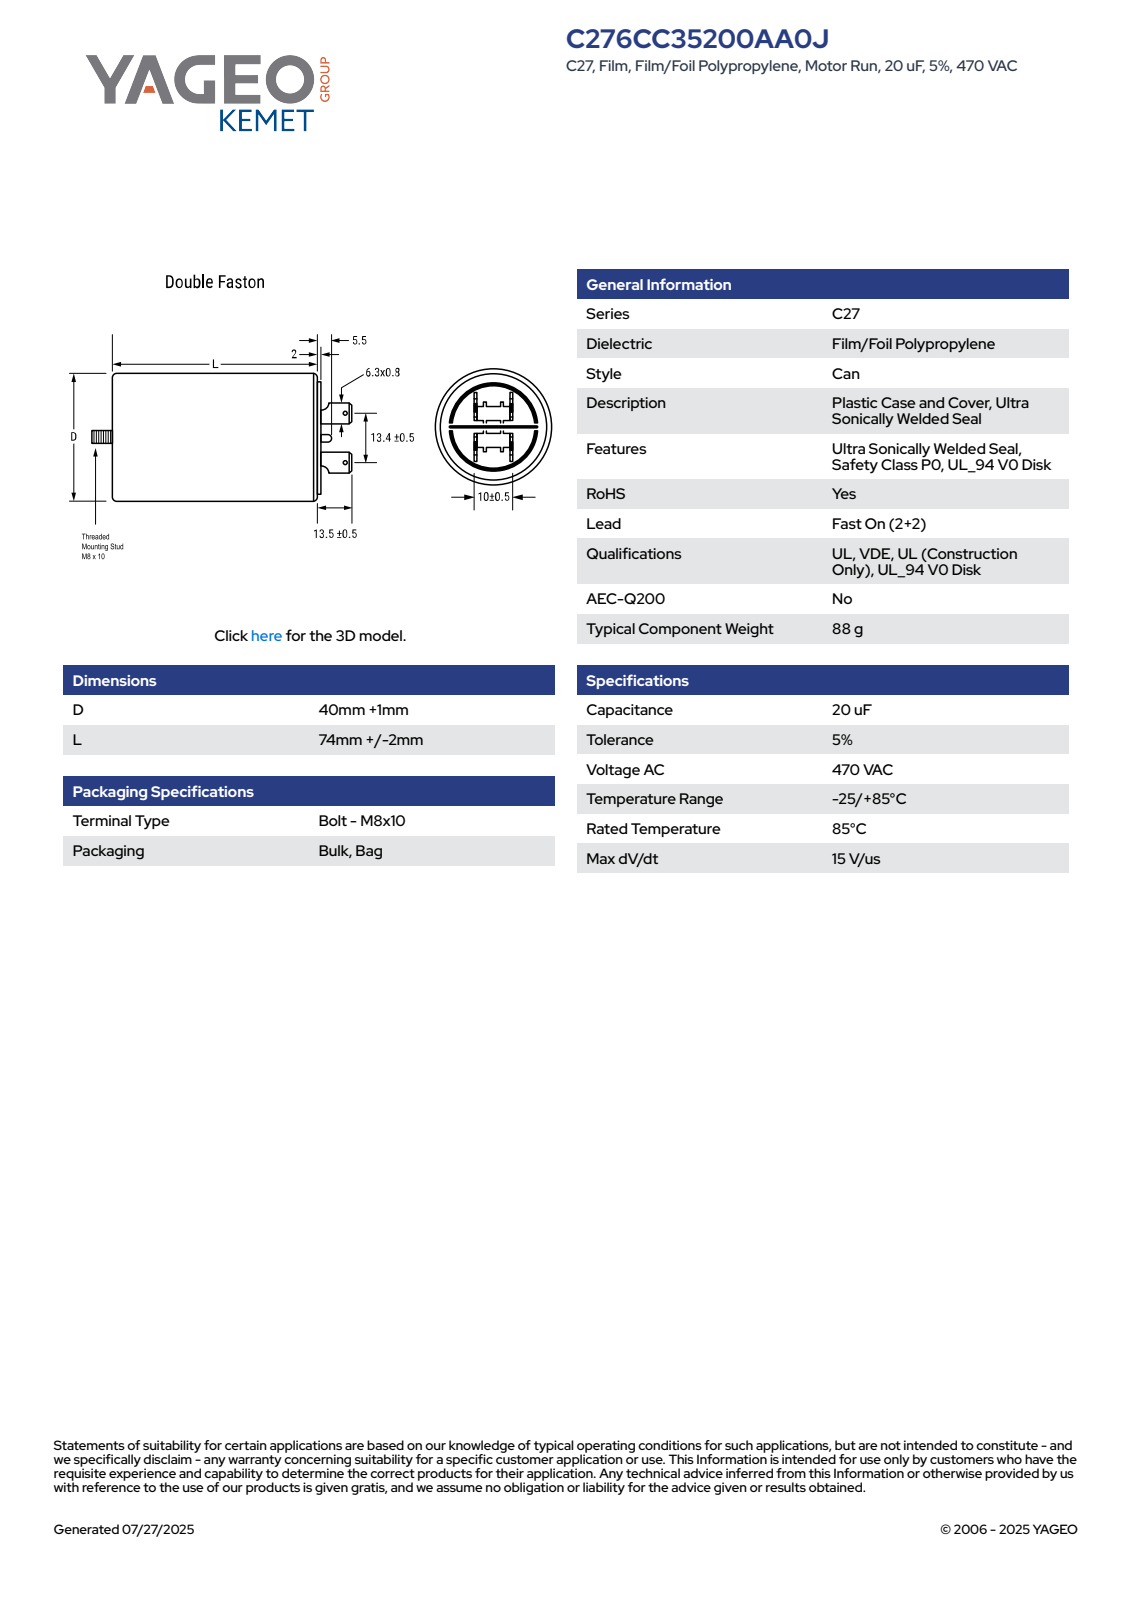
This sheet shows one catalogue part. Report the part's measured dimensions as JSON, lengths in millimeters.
{"part_name": "CFM_C27DF_40X74_D41L76", "step_written_by": "SolidWorks 2014 (AUTOMOTIVE_DESIGN)", "units": "millimeters", "bodies": {"solids": 1, "faces": 137, "planar": 49, "cylindrical": 53, "other": 35}, "overall_size": [100, 41, 41], "volume_mm3": 102466, "surface_area_mm2": 13529, "round_holes": [[1.2, 2]], "round_bosses_or_shafts": [[41, 1], [31.54, 1], [8, 1]], "partial_cylinders_radius": [[0.25, 9], [4, 2], [20.49, 1]], "face_to_face_distances": [78, 76, 2, 0.8, 9.7, 10.5, 8.9, 0.5, 10, 86], "hole_center_spacings": [13.9]}
